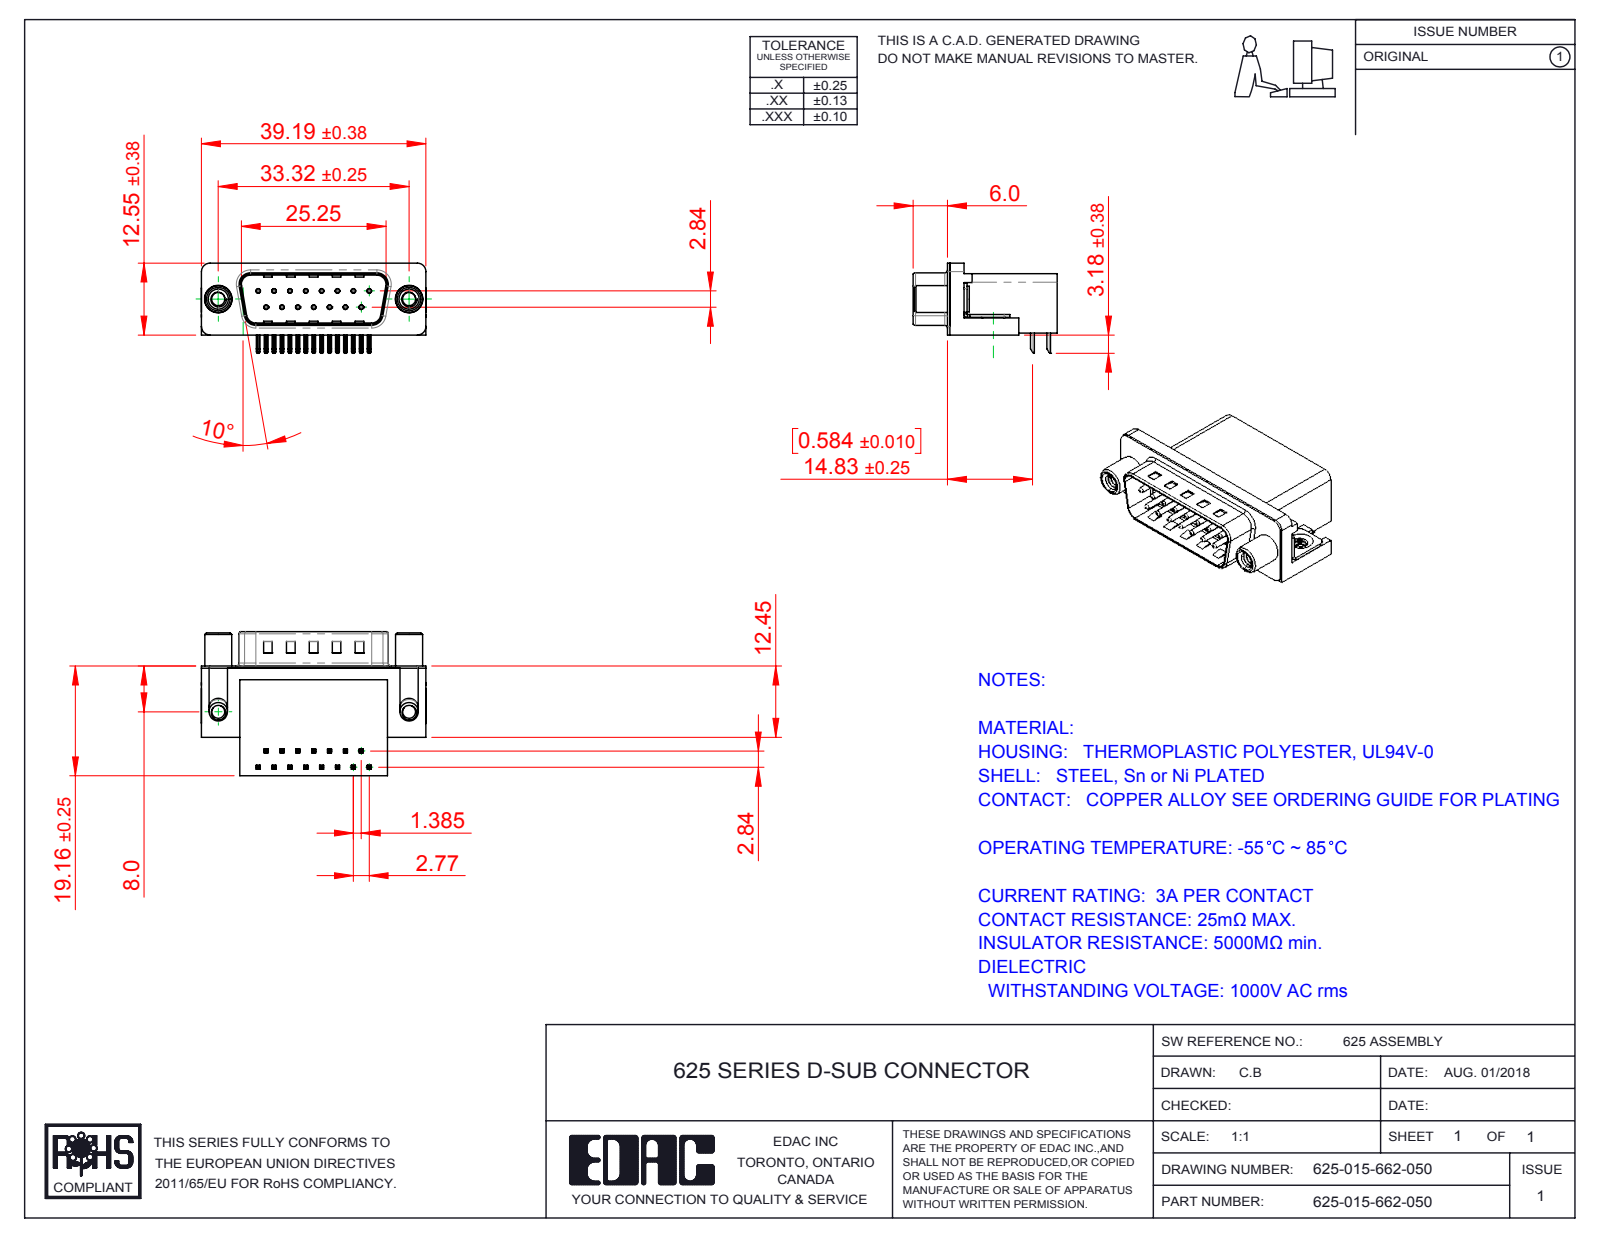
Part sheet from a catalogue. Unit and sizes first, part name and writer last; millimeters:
Units: millimetres
Overall size (bounding box): 39.22 × 25.16 × 15.73
Round holes (diameter × count): ⌀0.35 ×15, ⌀0.8 ×15, ⌀2.26 ×2, ⌀2.3 ×2, ⌀3.1 ×2, ⌀4 ×2, ⌀4.8 ×2, ⌀5 ×2
Round bosses / shafts (diameter × count): ⌀0.75 ×15, ⌀4.9 ×2, ⌀4.7 ×2, ⌀4.5 ×2, ⌀3.85 ×2, ⌀3.26 ×2
Partial cylindrical surfaces — rounded edges, fillets, slot ends (radius × count): R0.25 ×60, R0.12 ×30, R1 ×16, R0.5 ×9, R1.6 ×8, R1.5 ×6, R0.9 ×4, R2 ×4
Main face-to-face distances: 0.4, 10.35, 18.76, 2.1, 10.46, 1.7, 10.86, 19.16, 8.76, 16.26
Hole centre spacings: 3.16, 2.77, 5.54, 8.31, 11.08, 5.03, 5.04, 7.48
Volume: 6 344 mm³ · Surface area: 6 703 mm²
Bodies: 21 solids, 1505 faces (887 planar, 467 cylindrical, 151 other)
Part name (STEP PRODUCT): 625 4-40 Threaded Board Mount; 625 Contact Top; 625 Contact Bottom; 625 Shell_15 Socket (+3 more)
STEP written by: SolidWorks 2016 (CONFIG_CONTROL_DESIGN)
